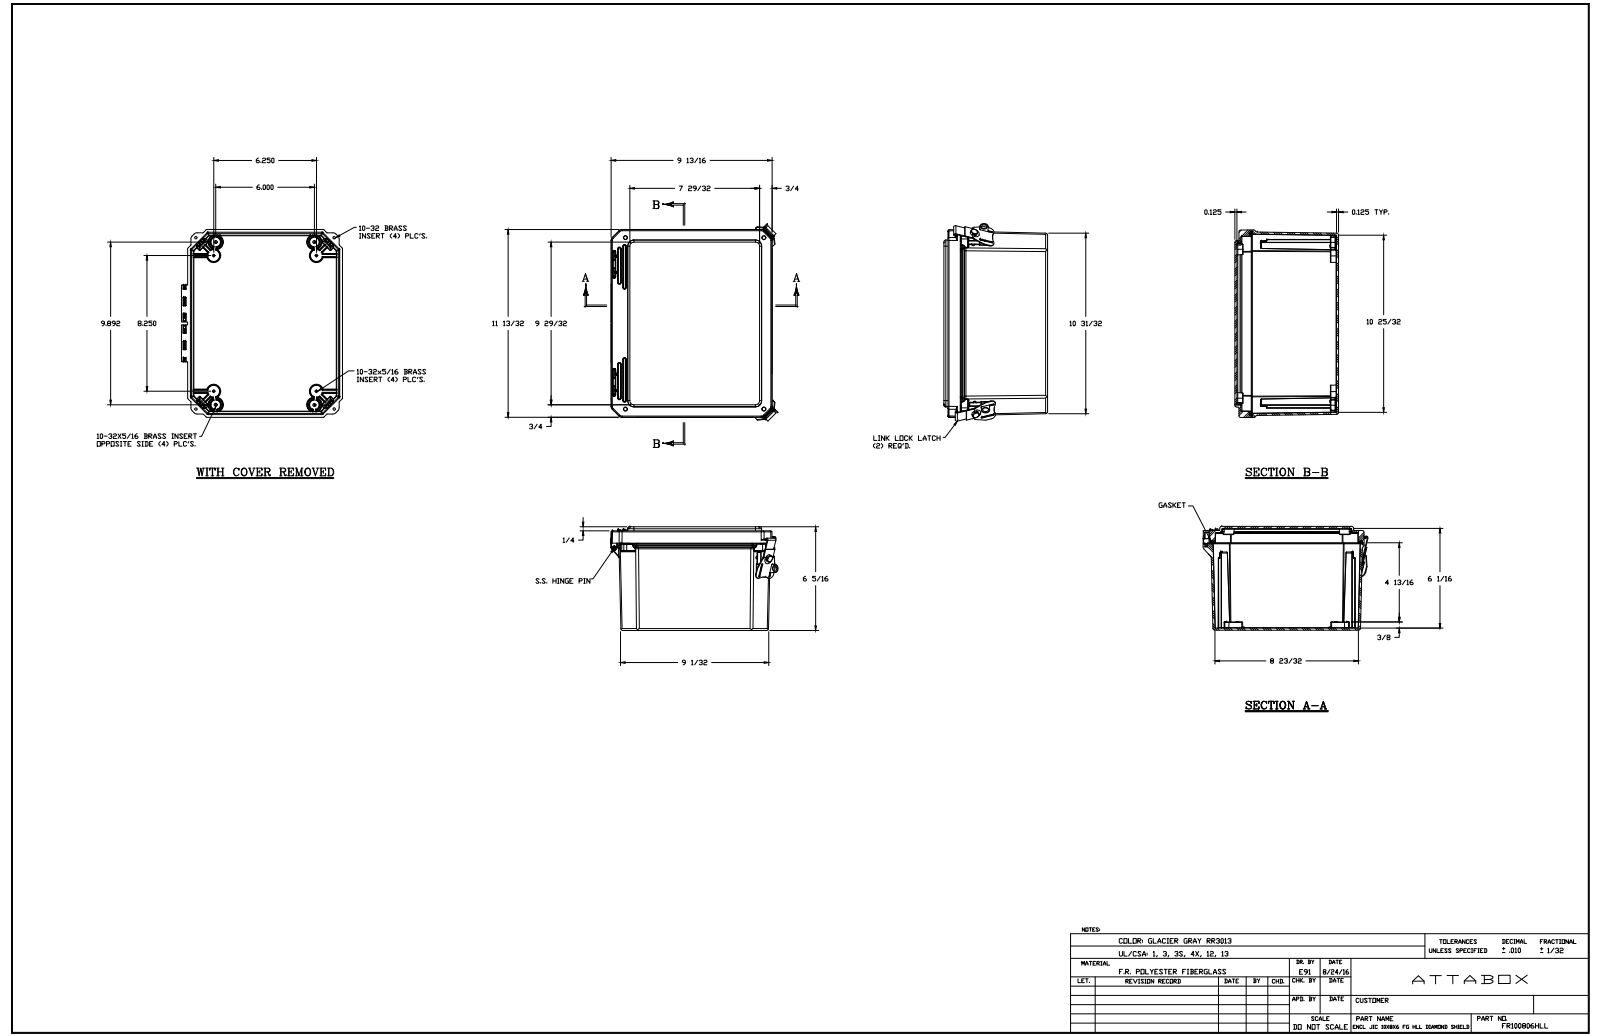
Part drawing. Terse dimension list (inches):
name: FR100806HLL
written by: SolidWorks 2018 (AUTOMOTIVE_DESIGN)
unit: in
bodies: 37 solids, 2247 faces (755 planar, 892 cylindrical, 600 other)
size: 12.339 × 10.256 × 6.31
volume: 70.92 in³; area: 1 015 in²
holes: 16× ⌀0.156, 8× ⌀0.152, 4× ⌀0.098, 4× ⌀0.15, 4× ⌀0.252, 4× ⌀0.253, 2× ⌀0.05, 2× ⌀0.12, 2× ⌀0.219, 2× ⌀0.227, 2× ⌀0.313, 2× ⌀0.363
bosses: 16× ⌀0.246, 4× ⌀0.87, 4× ⌀0.209, 4× ⌀0.2, 2× ⌀0.6, 2× ⌀0.135, 2× ⌀0.05, 1× ⌀0.435
rounds: 177× R0.01, 80× R0.005, 57× R0.02, 43× R0.03, 34× R0.125, 28× R0.039, 24× R0.03, 24× R0.09
face distances: 0.125, 6.185, 0.127, 0.126, 6.31, 6.061, 0.25, 5.935, 0.125, 6.06
hole spacings: 7.416, 11.874, 0.83, 6.18, 9.072, 9.399, 1.24, 1.536
